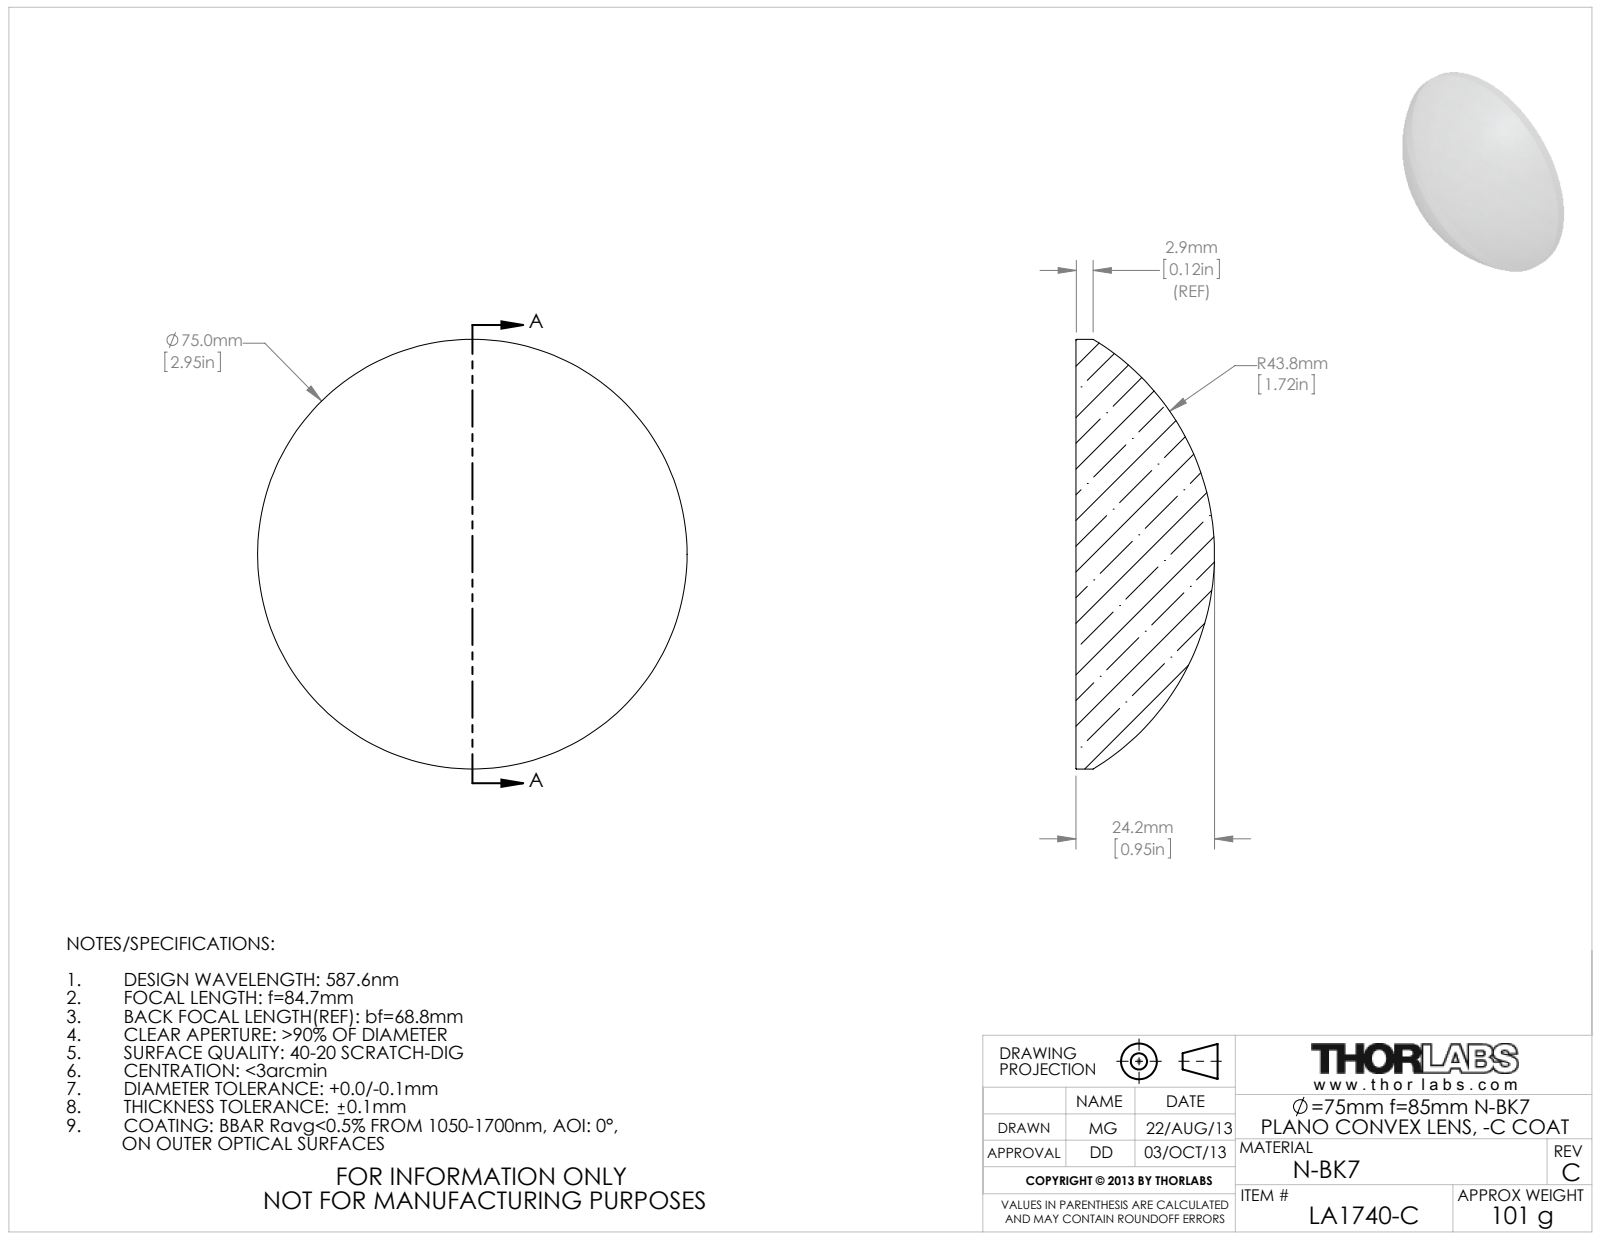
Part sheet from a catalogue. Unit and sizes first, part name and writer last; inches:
Units: inches
Overall size (bounding box): 2.953 × 2.953 × 0.952
Round bosses / shafts (diameter × count): ⌀2.953 ×1
Bodies: 0 solids, 5 faces (1 planar, 2 cylindrical, 2 other)
Part name (STEP PRODUCT): 4613-E0W
STEP written by: SolidWorks 2009 (AUTOMOTIVE_DESIGN)
